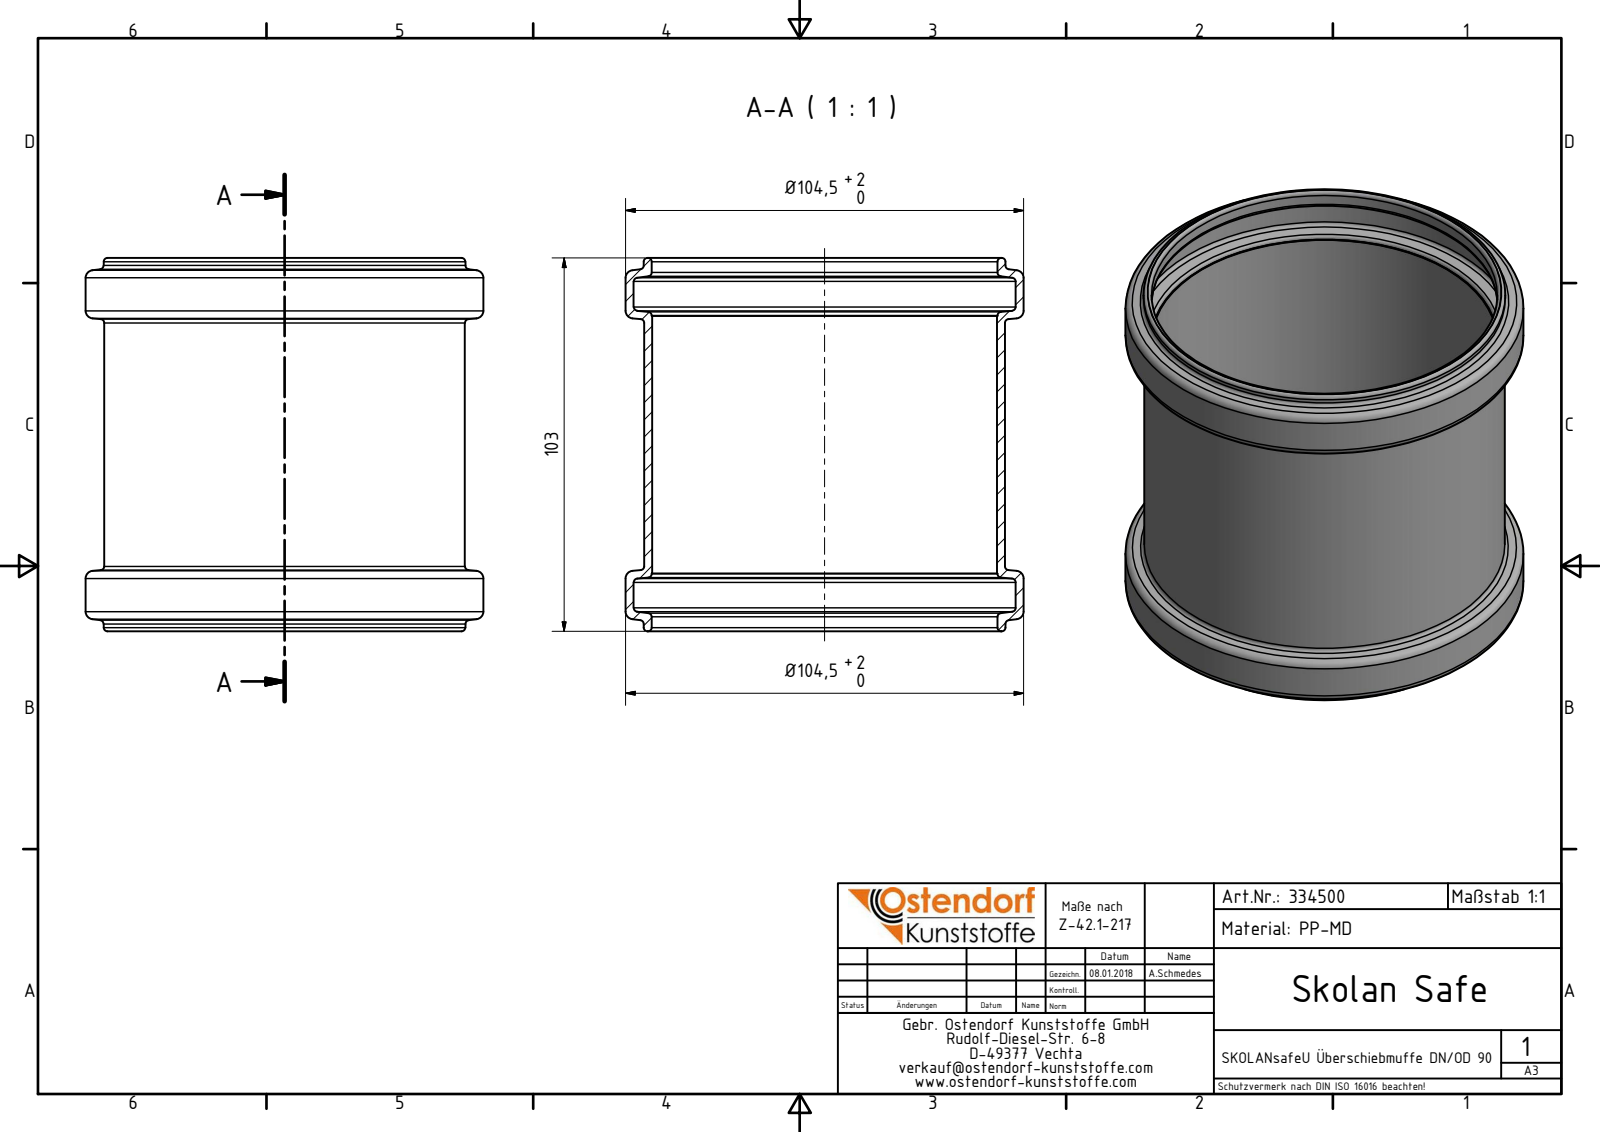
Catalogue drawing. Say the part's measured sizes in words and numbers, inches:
The part is named "334500 SKOLANsafeU Überschiebmuffe DN_OD 90". Its 3-D file was written by "Autodesk Inventor 2016 (AUTOMOTIVE_DESIGN)". It is 1 solid with 44 faces: 4 planar, 12 cylindrical and 28 other. Overall it measures 4.114 by 4.114 by 3.858 inches. Its volume is 4.363 cubic inches and its surface area 104.9 square inches. Round holes: 1 of diameter 3.563, 1 of diameter 3.575, 1 of diameter 3.949. Round bosses or shafts: 1 of diameter 4.114, 1 of diameter 3.74, 1 of diameter 3.728. The main face-to-face distances are 0.599, 3.259, 2.661, 3.858.
